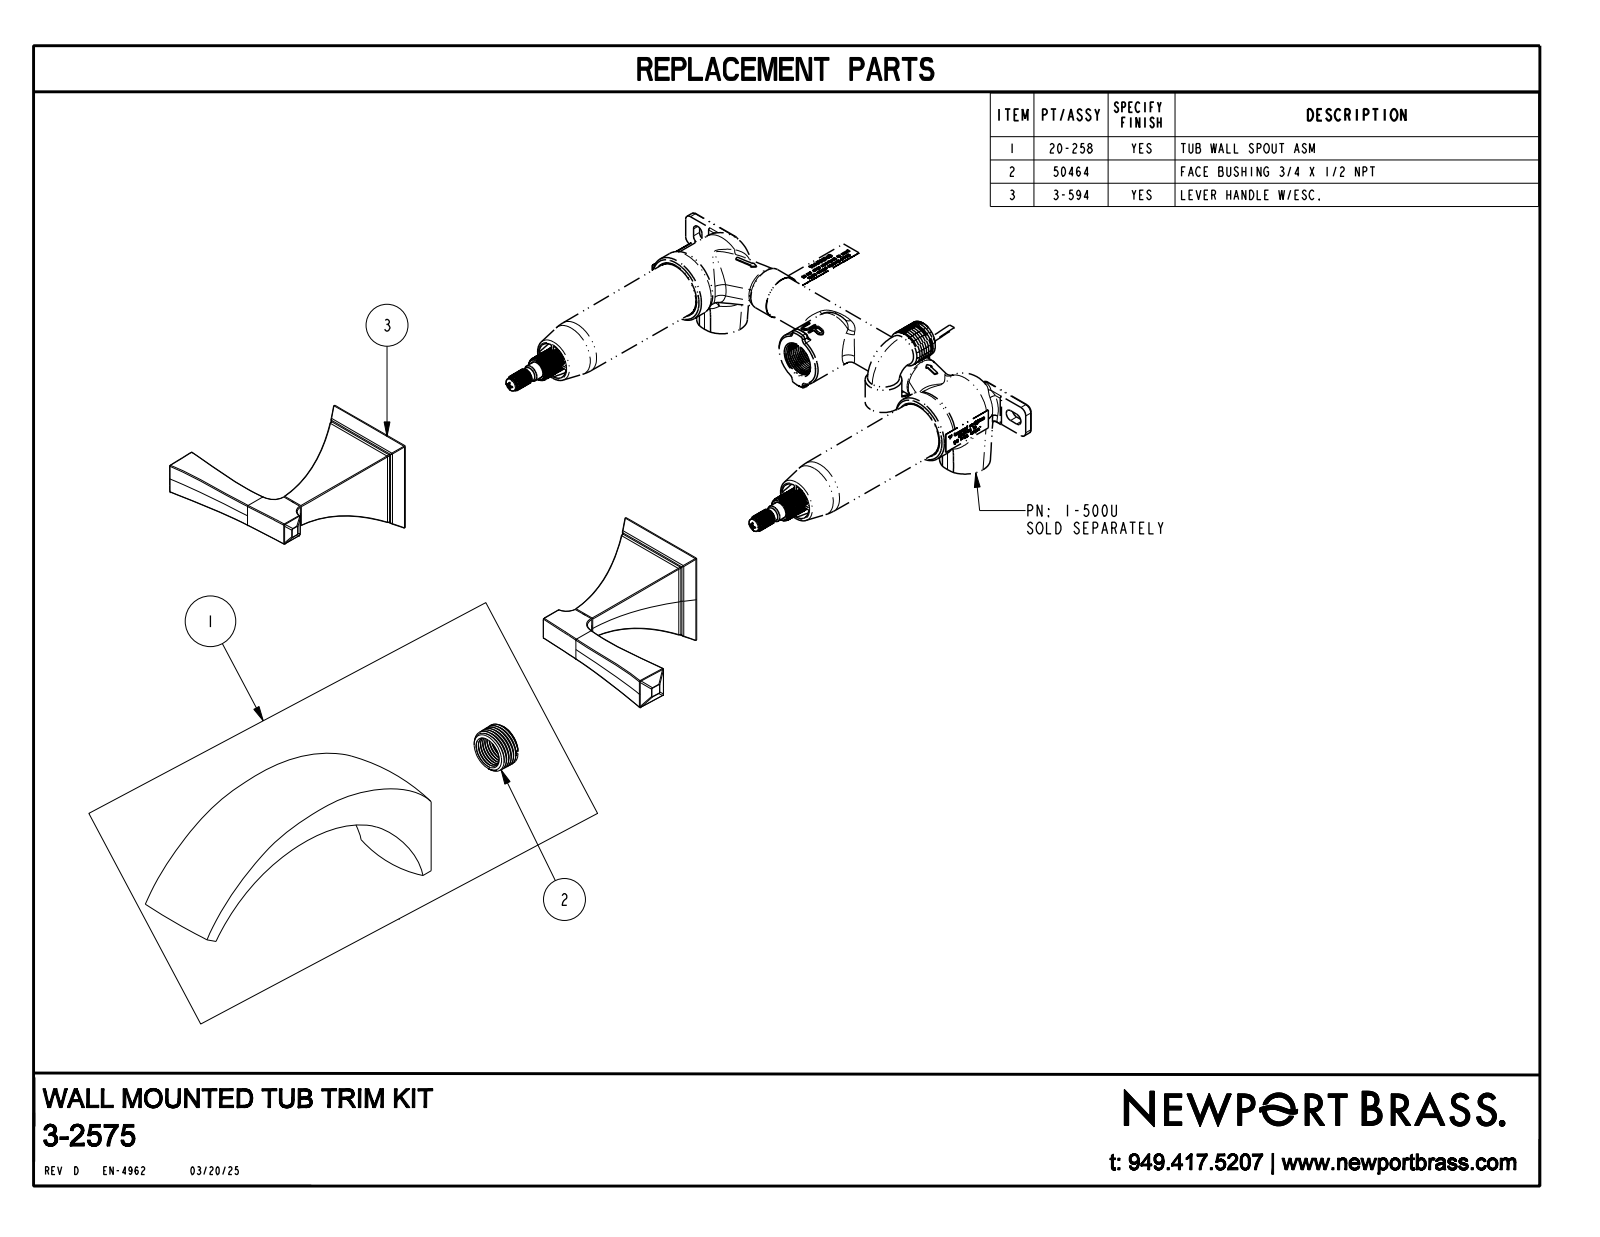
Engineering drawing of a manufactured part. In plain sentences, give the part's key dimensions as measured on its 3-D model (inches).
The part is named "3-2575_SW0001". Its 3-D file was written by "CREO PARAMETRIC BY PTC INC, 2018400 (AUTOMOTIVE_DESIGN)". It is 3 solids with 307 faces: 34 planar, 53 cylindrical and 220 other. Overall it measures 13.979 by 8.65 by 7.35 inches. Its volume is 25.92 cubic inches and its surface area 107.4 square inches. Round bosses or shafts: 2 of diameter 0.5. Partial cylindrical surfaces (rounded edges, fillets, slot ends): 32 of radius 0.02, 16 of radius 0.06, 1 of radius 5. The main face-to-face distances are 2, 0.56, 2.5, 2.531, 0.031, 5.501, 2.316, 4.316, 6.637, 4.321.
